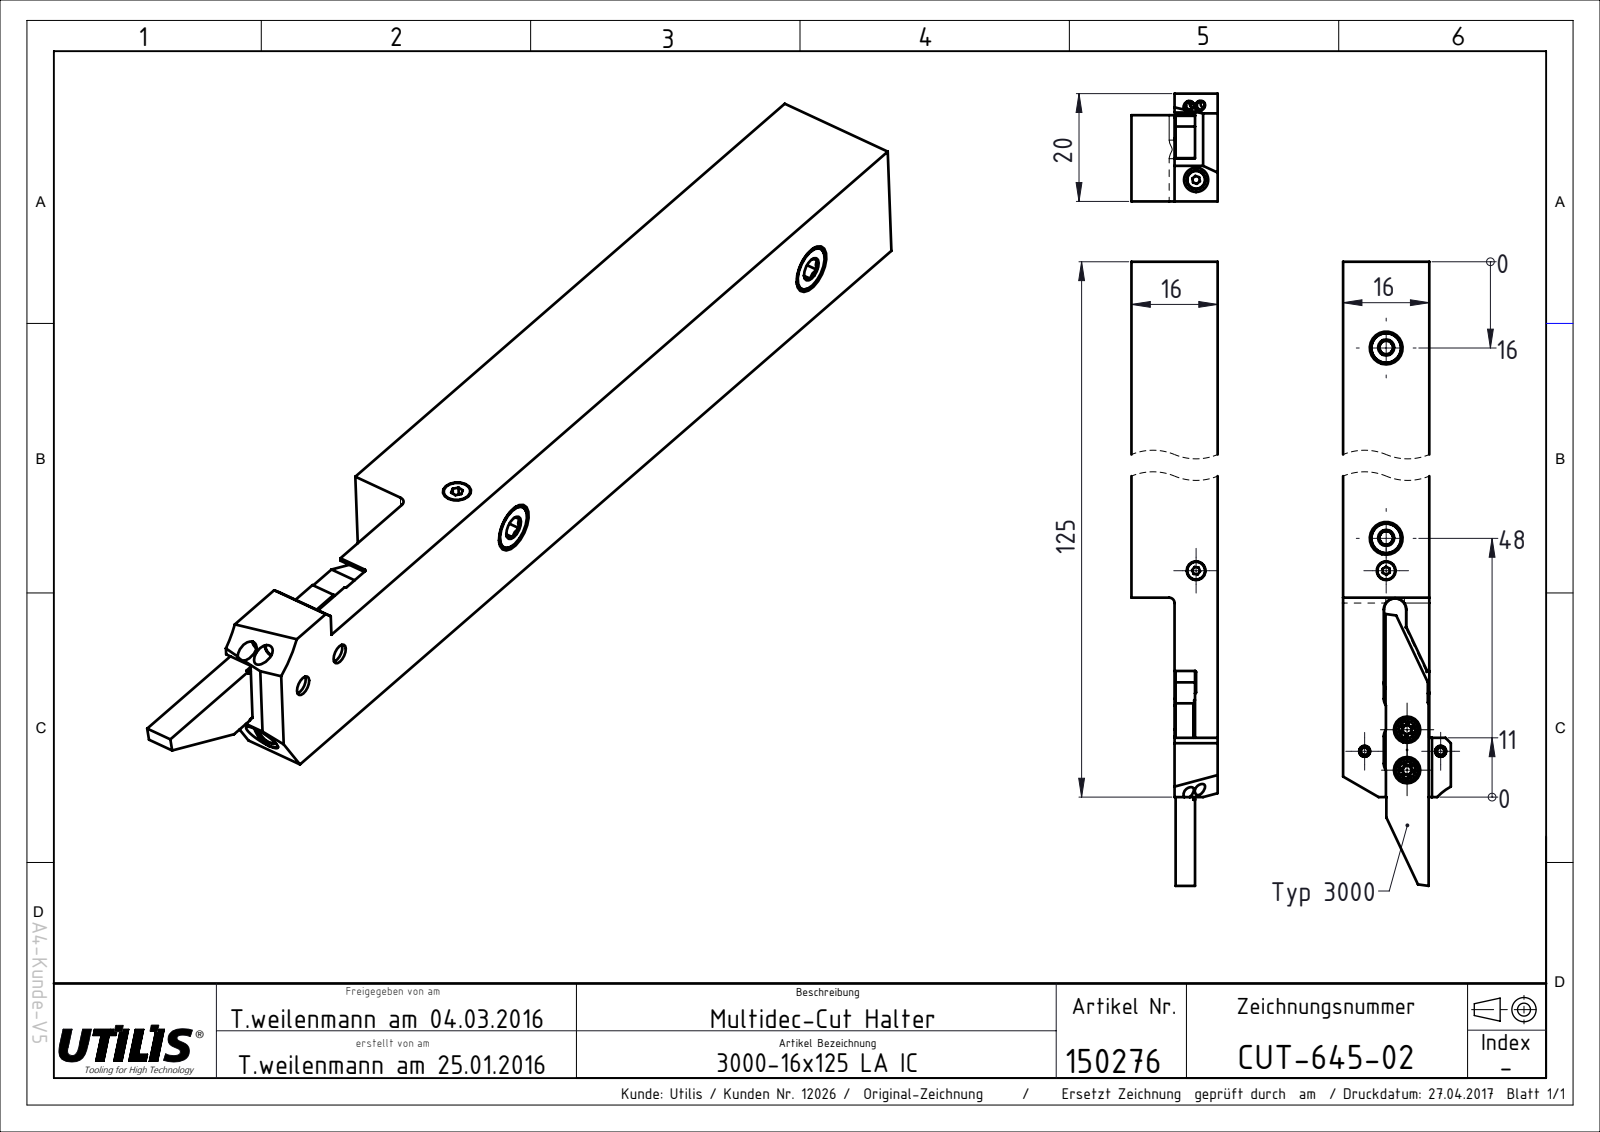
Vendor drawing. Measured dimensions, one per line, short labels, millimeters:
name: CUT-645-02
written by: SolidWorks 2016 (AUTOMOTIVE_DESIGN)
unit: mm
bodies: 1 solid, 153 faces (52 planar, 62 cylindrical, 39 other)
size: 141.47 × 20 × 16
volume: 27 539 mm³; area: 8 997 mm²
holes: 2× ⌀3.55
bosses: 2× ⌀4.1, 2× ⌀3
rounds: 19× R0.2, 12× R0.45, 5× R2.1, 2× R0.15, 1× R1, 1× R10
face distances: 16, 8, 8.2, 7.8, 3.8, 4, 4.2, 11.8, 3.6, 15.88
hole spacings: 7.5
